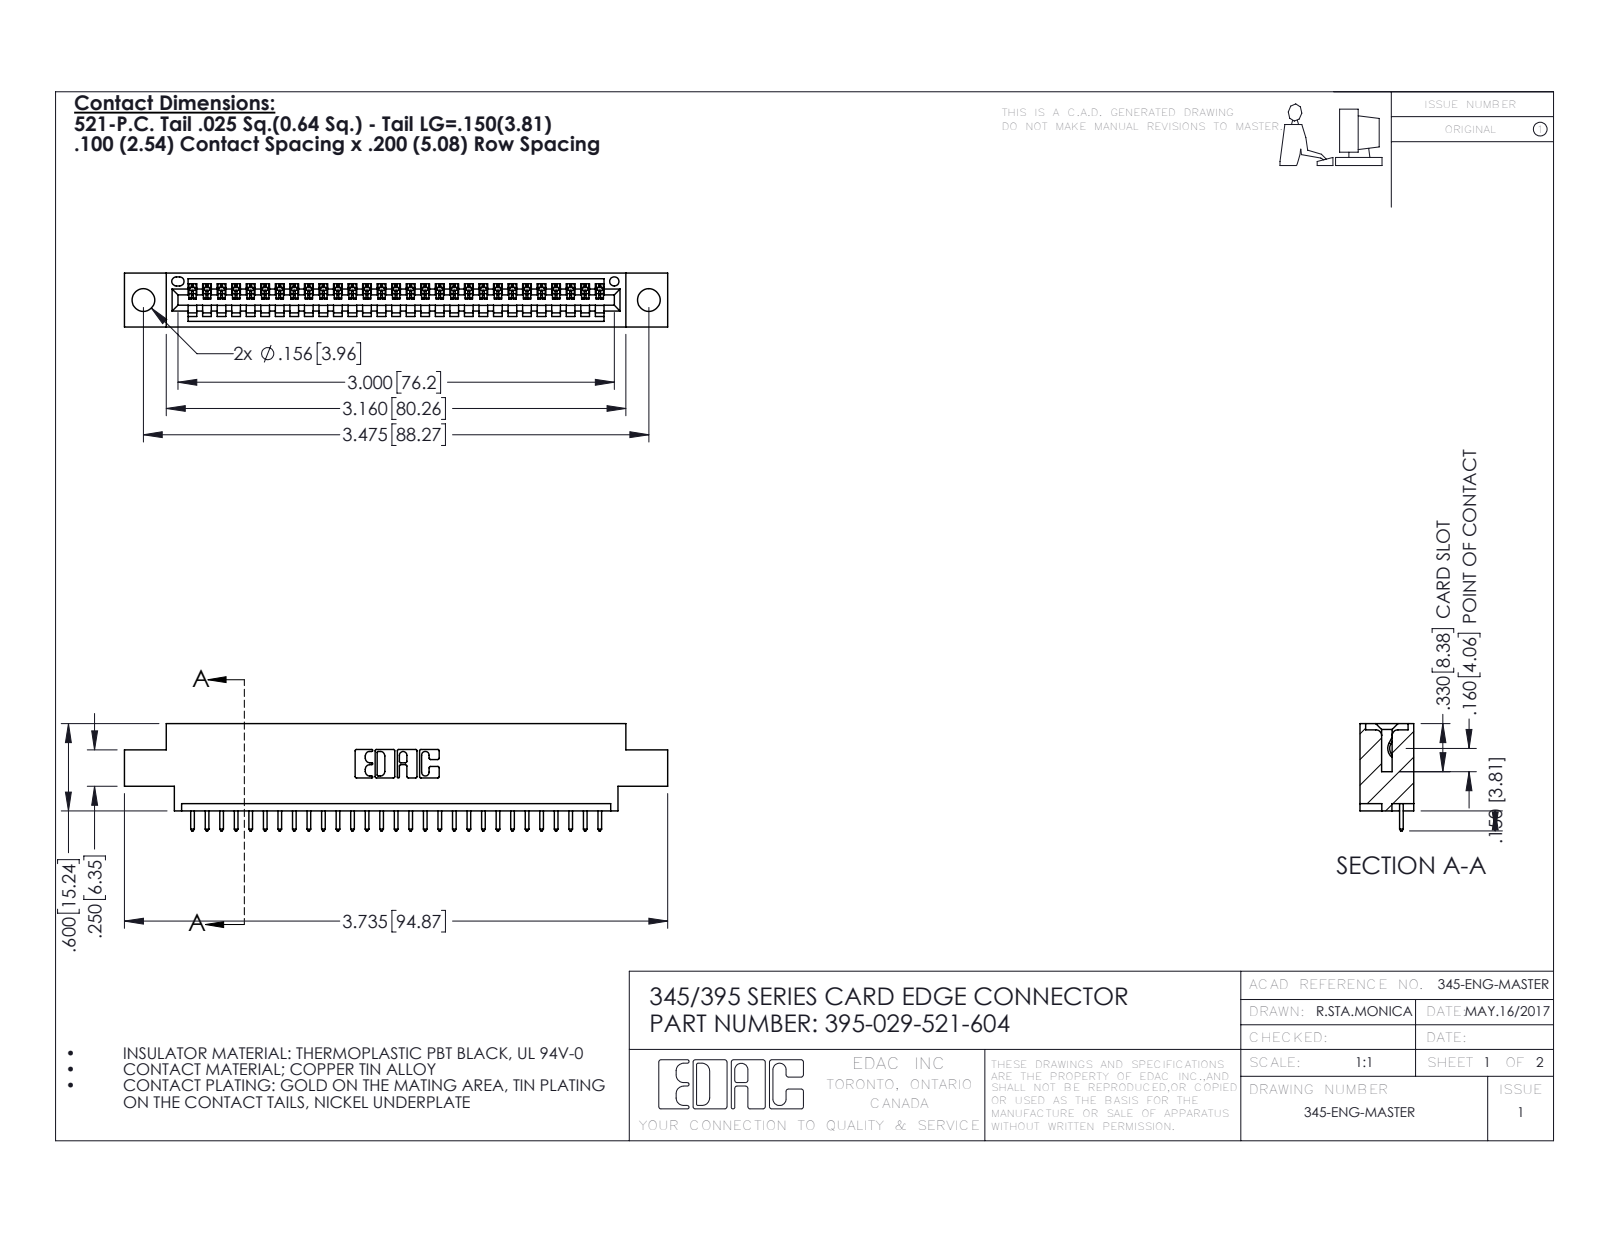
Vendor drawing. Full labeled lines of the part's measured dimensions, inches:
Part name (STEP PRODUCT): 345 Part_0.170 Offset - 0.156 Dia-TH; 395-029-521-604; 345-292-001_345-293-121
STEP written by: SolidWorks 2016 (CONFIG_CONTROL_DESIGN)
Units: inches
Bodies: 30 solids, 1812 faces (1244 planar, 568 cylindrical, 0 other)
Overall size (bounding box): 3.735 × 0.737 × 0.37
Volume: 0.526 in³ · Surface area: 16.88 in²
Round holes (diameter × count): ⌀0.156 ×2, ⌀0.064 ×1
Partial cylindrical surfaces — rounded edges, fillets, slot ends (radius × count): R0.006 ×58, R0.01 ×58, R0.01 ×22, R0.007 ×6, R0.031 ×6, R0.026 ×3, R0.031 ×2, R0.04 ×2
Main face-to-face distances: 0.298, 0.072, 0.37, 0.2, 0.098, 0.272, 0.025, 0.225, 0.175, 0.149
Hole centre spacings: 0.27, 3.24, 3.475
